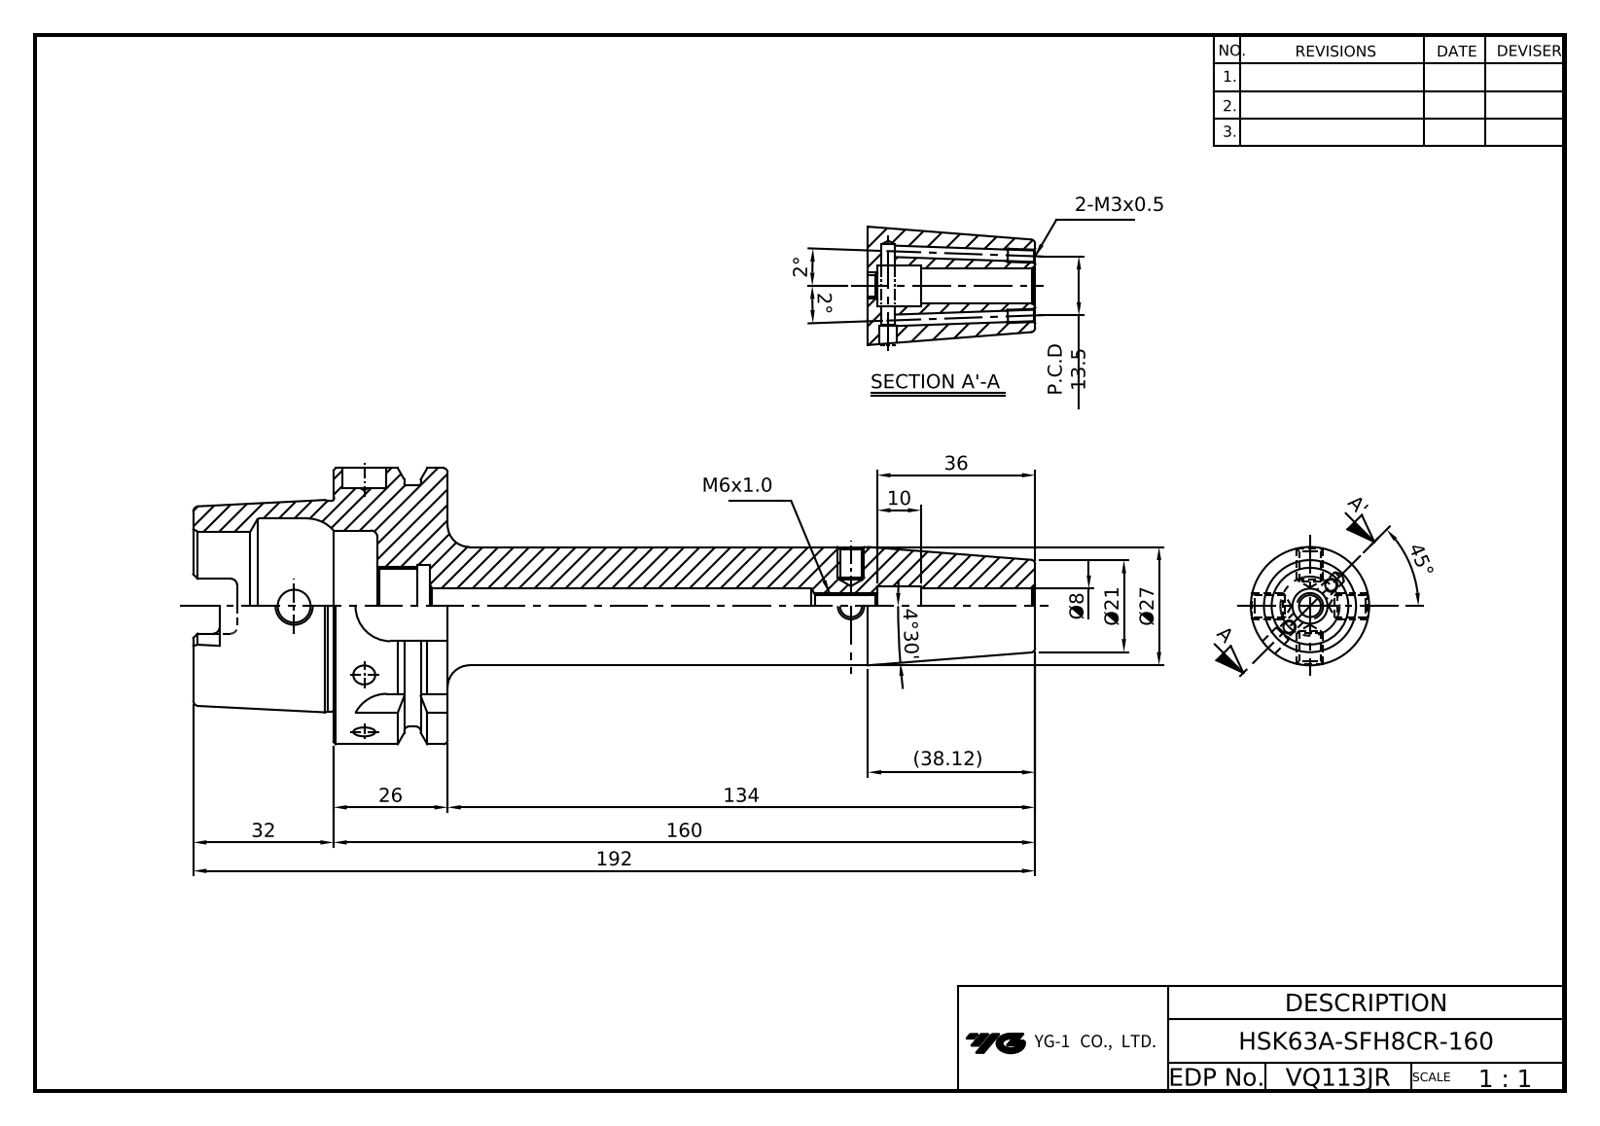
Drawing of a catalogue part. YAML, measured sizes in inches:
part_name: "LO-HSK63A-SFH8CR-160"
step_written_by: "Autodesk Inventor 2022 (AUTOMOTIVE_DESIGN)"
units: inches
bodies: {solids: 1, faces: 121, planar: 42, cylindrical: 36, other: 43}
overall_size: [7.559, 2.48, 2.48]
volume: 8.996
surface_area: 56.93
round_holes:
  - {diameter: 0.097, count: 2}
  - {diameter: 0.194, count: 1}
  - {diameter: 0.295, count: 1}
  - {diameter: 0.315, count: 1}
  - {diameter: 0.362, count: 1}
  - {diameter: 0.394, count: 1}
  - {diameter: 0.666, count: 1}
  - {diameter: 0.748, count: 1}
  - {diameter: 1.339, count: 1}
  - {diameter: 1.575, count: 1}
round_bosses_or_shafts:
  - {diameter: 2.48, count: 1}
  - {diameter: 2.165, count: 1}
  - {diameter: 1.891, count: 1}
  - {diameter: 1.063, count: 1}
partial_cylinders:
  - {radius: 0.059, count: 6}
  - {radius: 0.113, count: 4}
  - {radius: 0.315, count: 4}
face_to_face_distances: [1.024, 0.394, 0.63, 1.26, 1.654, 2.283, 2.087, 0.866, 0.157, 0.472]
